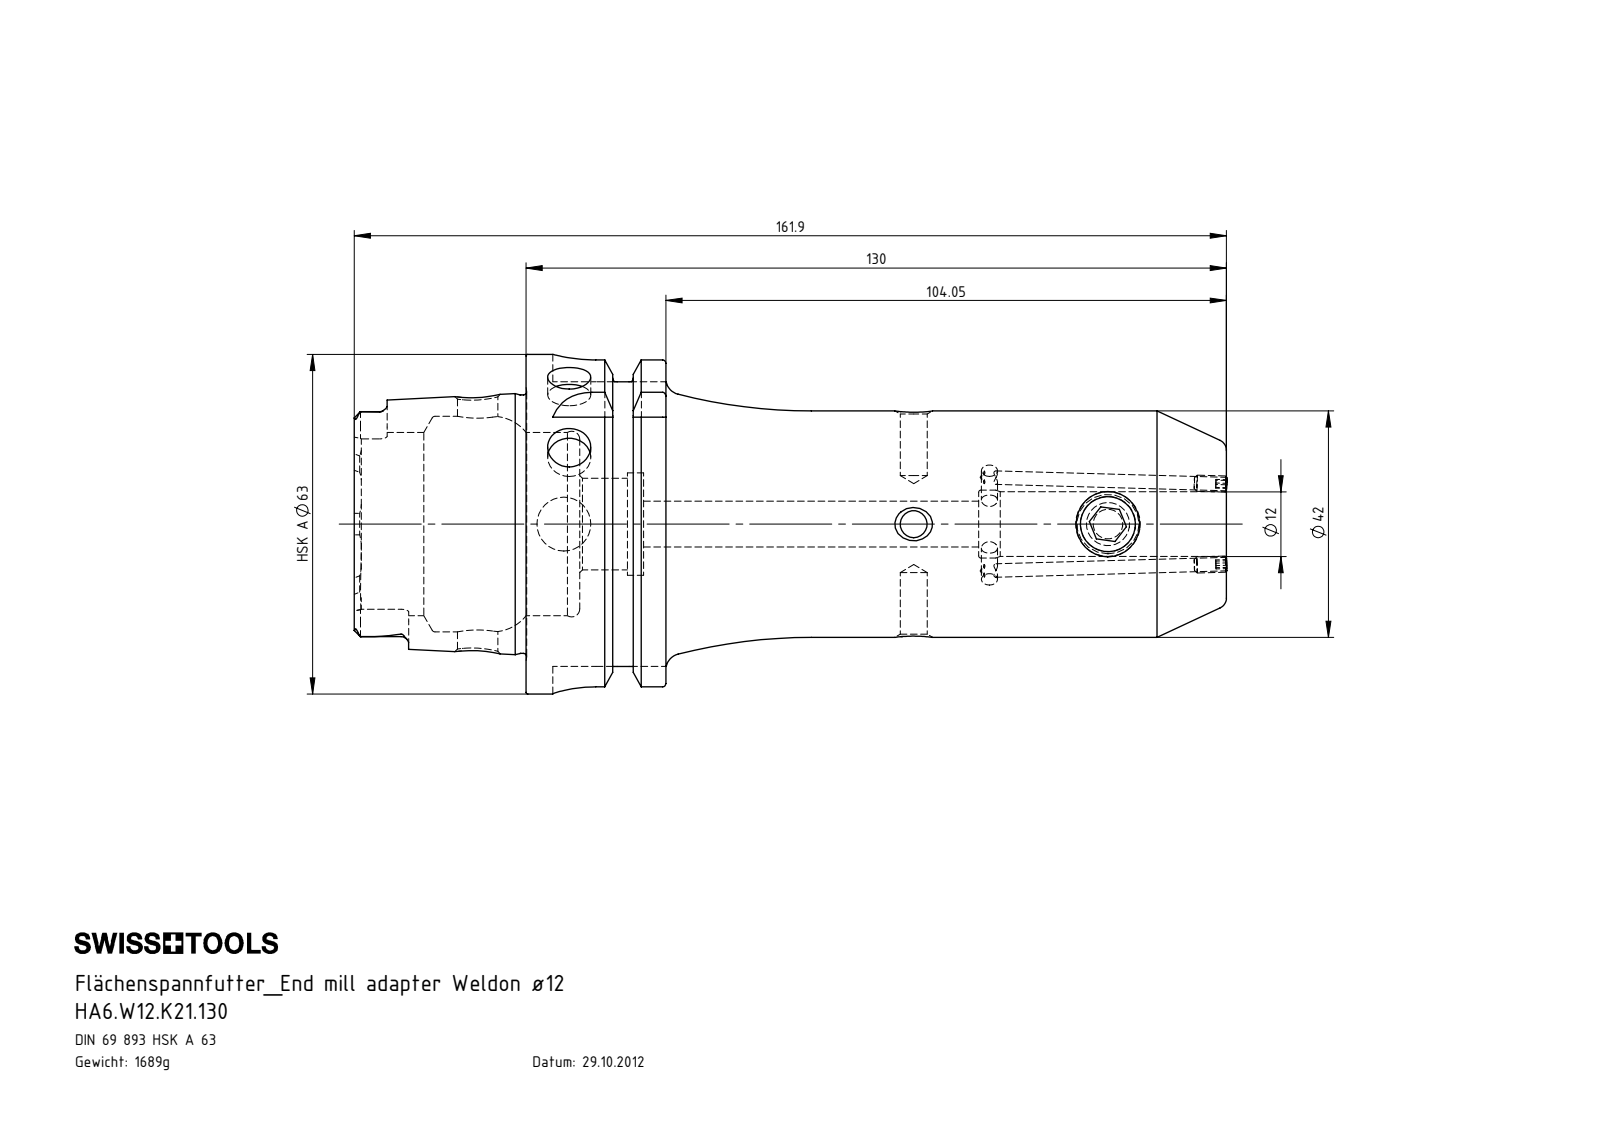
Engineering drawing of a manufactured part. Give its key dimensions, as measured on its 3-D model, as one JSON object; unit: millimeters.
{"part_name": "HA6-W12.K21.130; ERU-CJ2.001.006; W12-ER1.001.016; HA6-W12.K21.130_A_Fertigbearbeitung", "step_written_by": "SolidWorks 2012 (CONFIG_CONTROL_DESIGN)", "units": "millimeters", "bodies": {"solids": 4, "faces": 289, "planar": 78, "cylindrical": 81, "other": 130}, "overall_size": [161.98, 63, 63], "volume_mm3": 215113, "surface_area_mm2": 41274, "round_holes": [[2.5, 2], [5, 2], [8, 2], [3, 1], [7.5, 1], [8.5, 1], [10, 1], [10.25, 1], [12, 1], [12.6, 1], [17, 1], [19, 1]], "round_bosses_or_shafts": [[3, 2], [63, 1], [54.95, 1], [47.94, 1], [42, 1], [12, 1]], "partial_cylinders_radius": [[1.4, 6], [2.88, 4], [8, 4]], "face_to_face_distances": [25.95, 16, 9.95, 130, 120.05, 104.05, 31.9, 41.85, 57.85, 161.9], "hole_center_spacings": [36.05, 64.95, 80.95, 101]}
